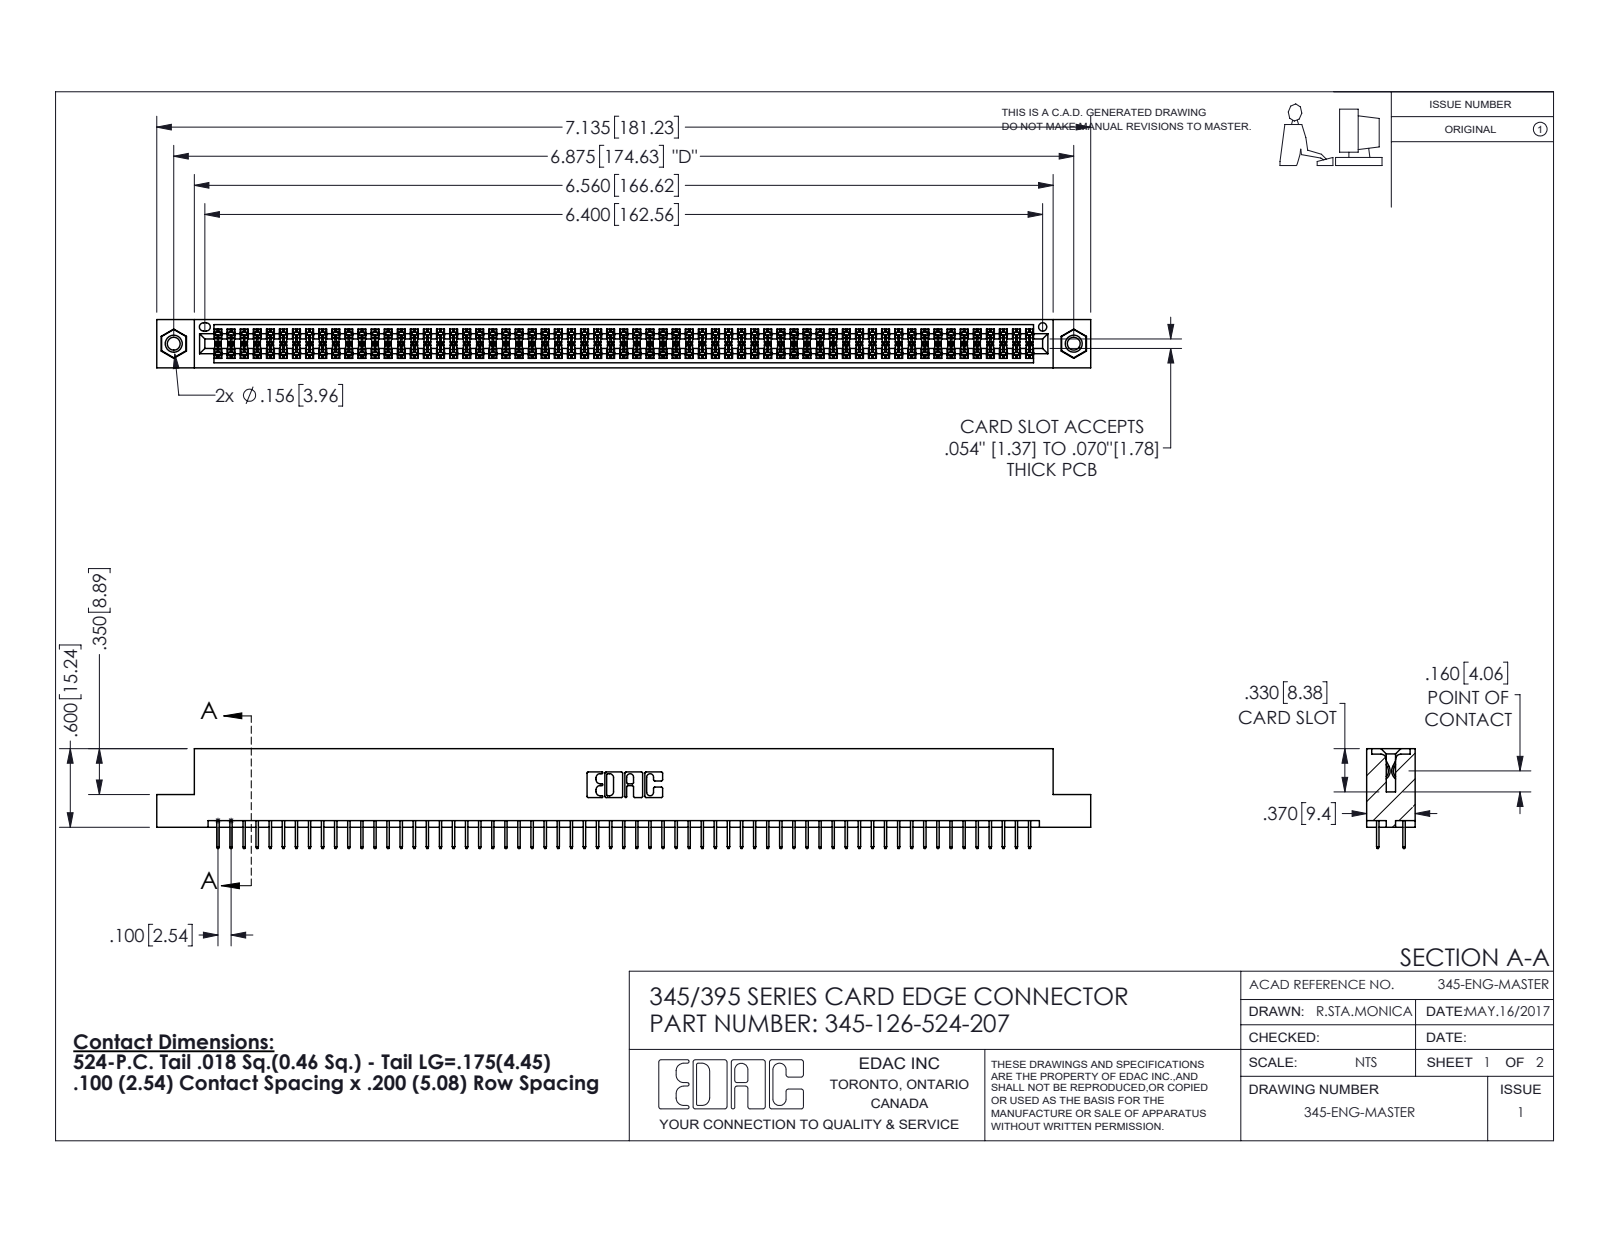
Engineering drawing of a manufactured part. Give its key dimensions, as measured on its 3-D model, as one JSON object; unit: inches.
{"part_name": "345-126-524-207; 345 Part_Flush Mounting Lugs - 0.156 Dia-TI; 345-250-001_345-250-005-103; 345-292-001_345-293-124", "step_written_by": "SolidWorks 2016 (CONFIG_CONTROL_DESIGN)", "units": "inches", "bodies": {"solids": 129, "faces": 6990, "planar": 5026, "cylindrical": 1948, "other": 16}, "overall_size": [7.135, 0.762, 0.37], "volume_in3": 1.074, "surface_area_in2": 40.21, "round_holes": [[0.098, 2], [0.125, 2], [0.156, 2], [0.064, 1]], "round_bosses_or_shafts": [[0.155, 2]], "partial_cylinders_radius": [[0.006, 189], [0.01, 22], [0.007, 6], [0.031, 6], [0.026, 3], [0.014, 2], [0.019, 2], [0.022, 2]], "face_to_face_distances": [0.072, 0.298, 0.2, 0.37, 0.098, 0.272, 0.025, 0.225, 0.072, 0.175], "hole_center_spacings": [0.27, 6.639, 6.875]}
